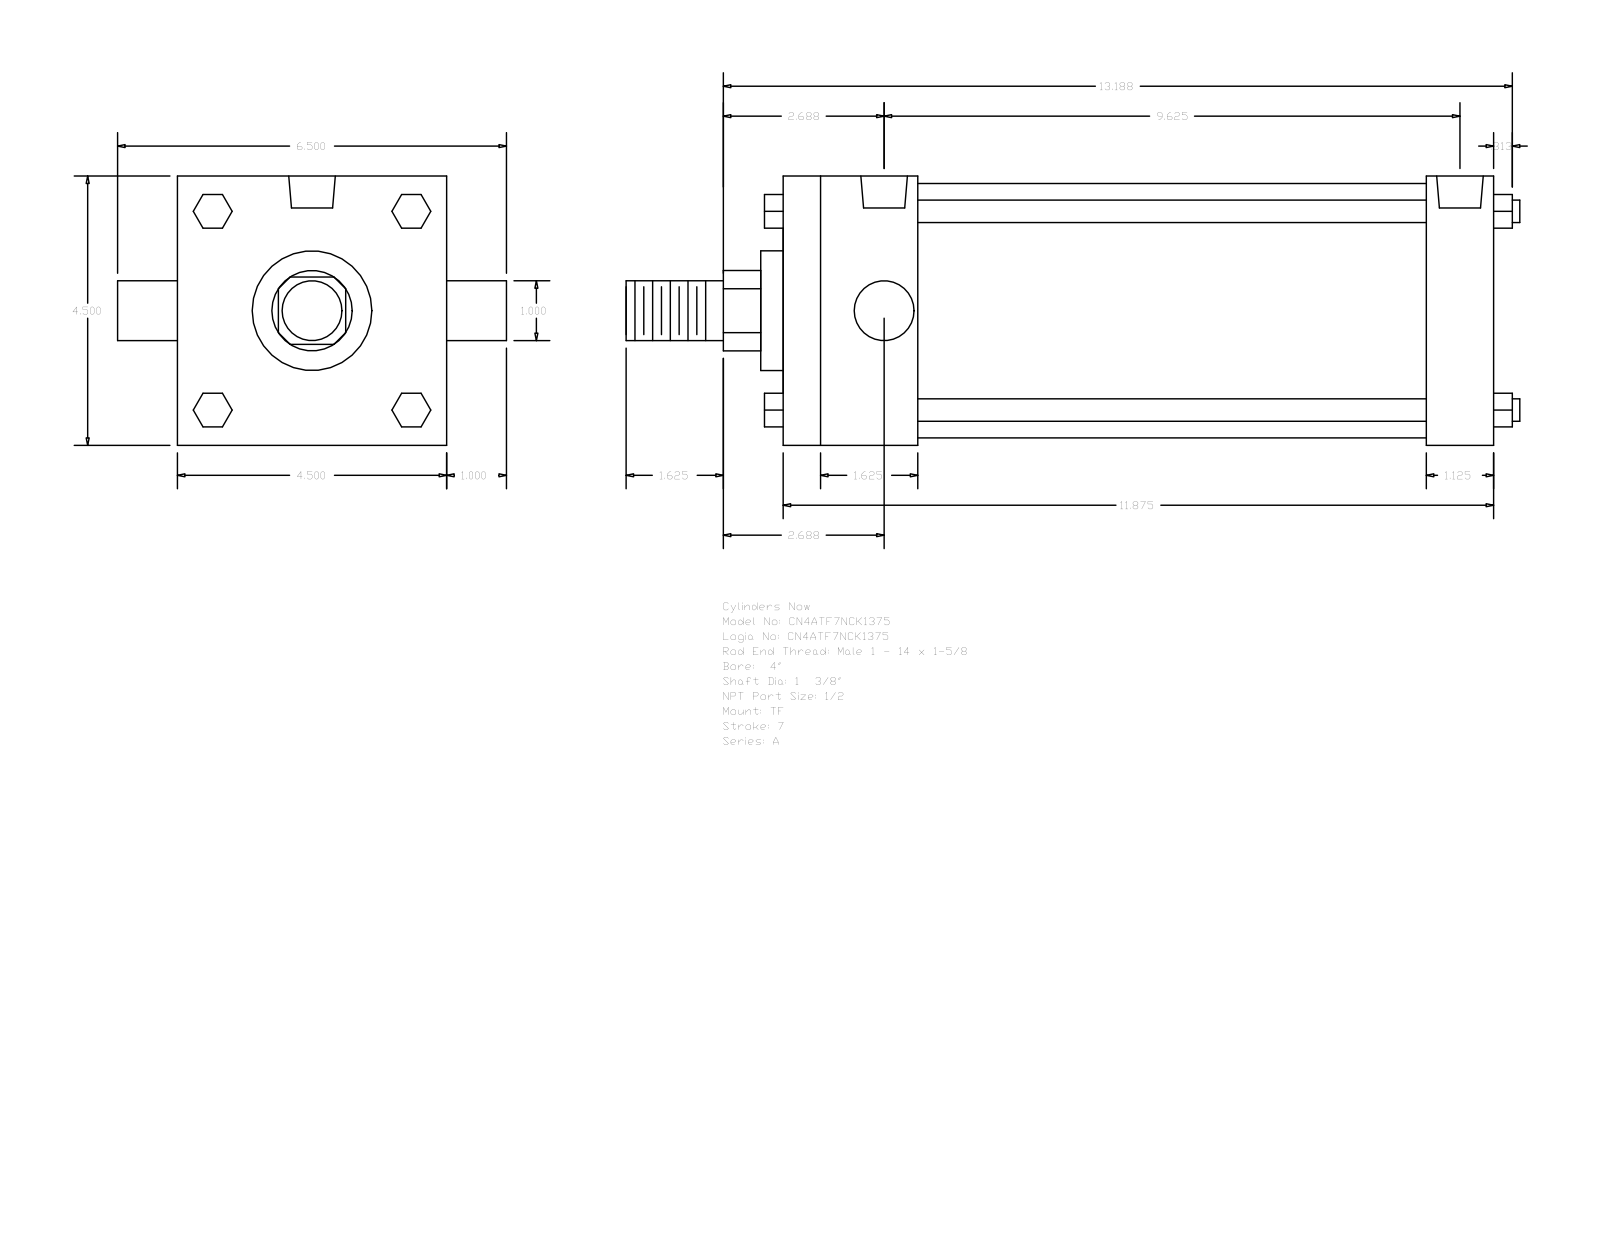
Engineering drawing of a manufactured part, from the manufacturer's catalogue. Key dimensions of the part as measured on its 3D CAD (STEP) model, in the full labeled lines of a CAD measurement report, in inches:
Part name (STEP PRODUCT): A_TF__0400_1.375
STEP written by: GSSL Pune (CONFIG_CONTROL_DESIGN)
Units: inches
Bodies: 0 solids, 120 faces (92 planar, 28 cylindrical, 0 other)
Overall size (bounding box): 14.937 × 6.5 × 4.5
Round holes (diameter × count): ⌀0.344 ×3, ⌀0.778 ×2
Round bosses / shafts (diameter × count): ⌀0.375 ×4, ⌀1 ×2, ⌀4.25 ×1, ⌀2 ×1, ⌀1.375 ×1
Partial cylindrical surfaces — rounded edges, fillets, slot ends (radius × count): R0.672 ×1
Main face-to-face distances: 4.5, 11.875, 2.25, 10.75, 1.125, 8.5, 9.625, 2.625, 0.563, 1
Hole centre spacings: 0.125, 9.5, 9.375, 9.625
